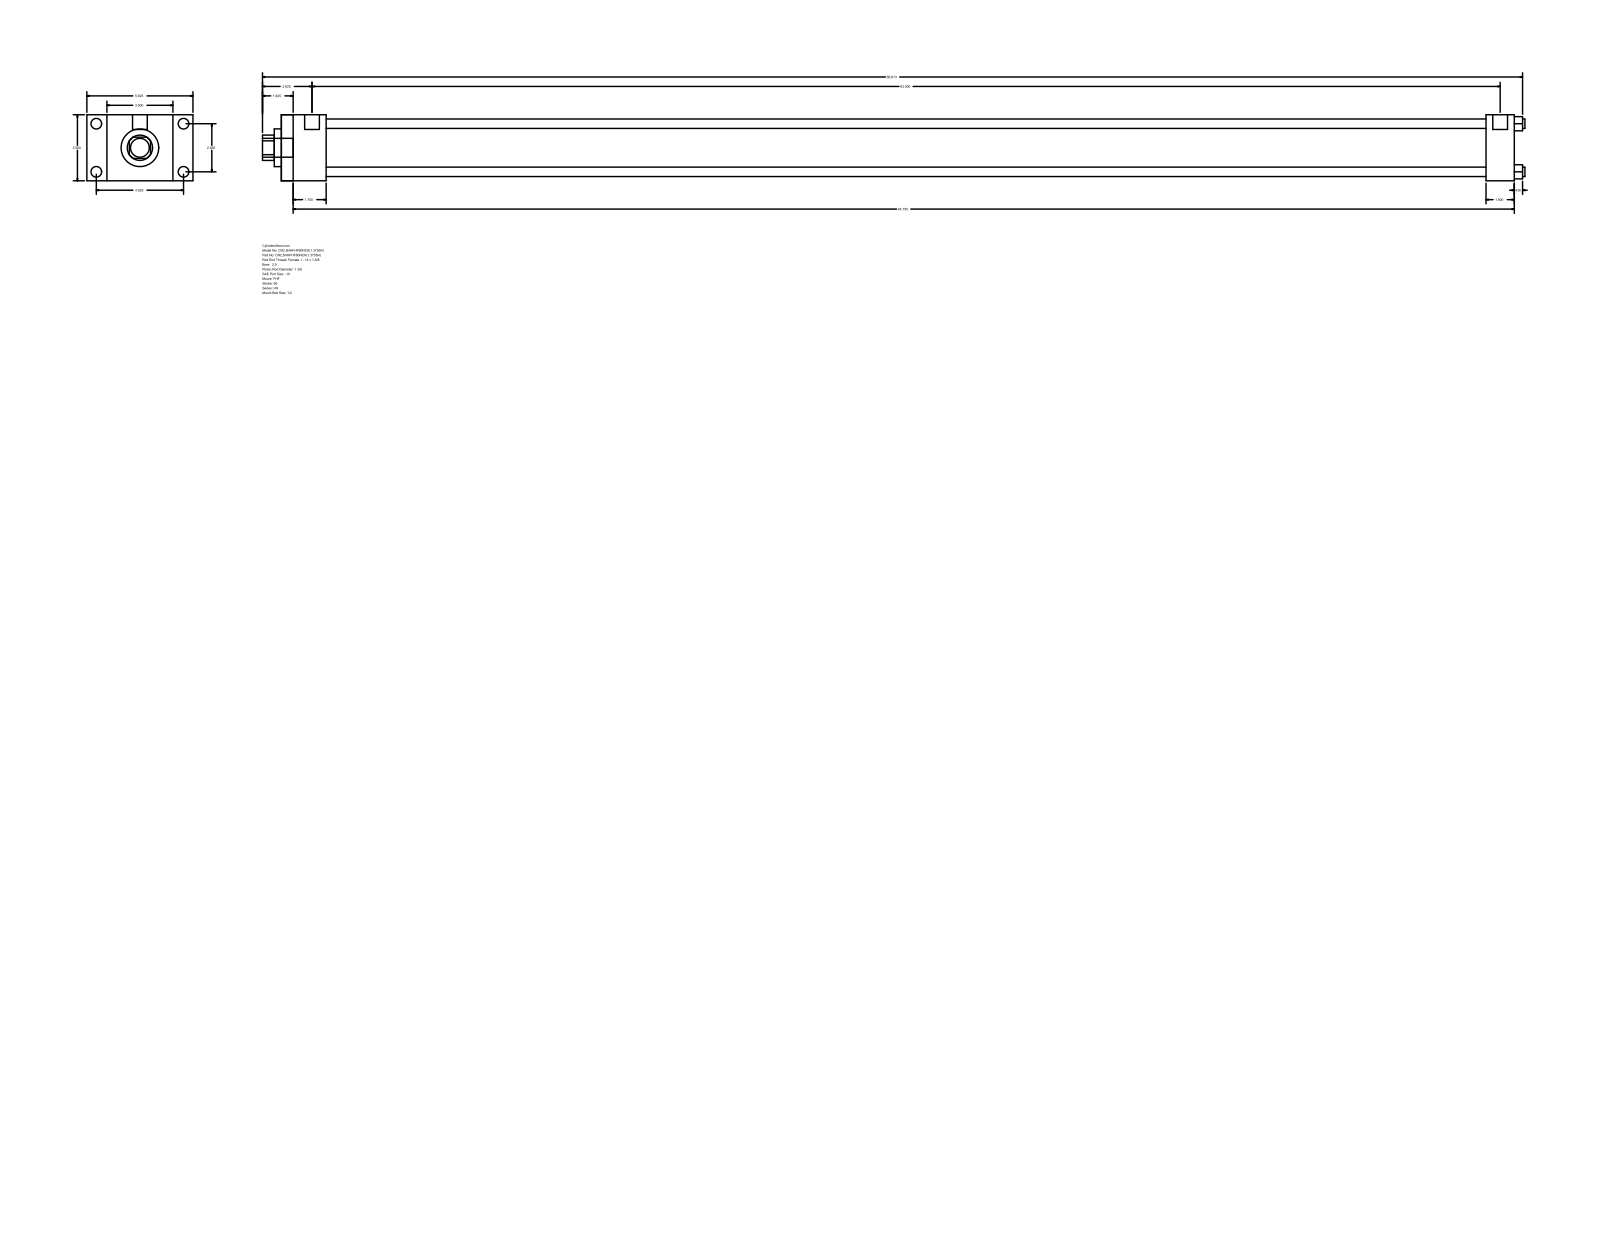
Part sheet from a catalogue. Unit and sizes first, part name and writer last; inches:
Units: inches
Overall size (bounding box): 66.937 × 5.625 × 3.5
Round holes (diameter × count): ⌀0.5 ×4, ⌀1.375 ×1, ⌀2 ×1, ⌀2.875 ×1
Round bosses / shafts (diameter × count): ⌀0.563 ×4, ⌀0.219 ×4, ⌀0.781 ×2, ⌀1 ×1
Partial cylindrical surfaces — rounded edges, fillets, slot ends (radius × count): R0.672 ×1
Main face-to-face distances: 3.5, 2.375, 1.063, 4.563, 65.375, 63, 5.625, 63.875, 61.5, 1.5
Hole centre spacings: 1.803, 2.55, 3.606
Bodies: 0 solids, 88 faces (60 planar, 28 cylindrical, 0 other)
Part name (STEP PRODUCT): HH_FHF__0250_1.375
STEP written by: GSSL Pune (CONFIG_CONTROL_DESIGN)
